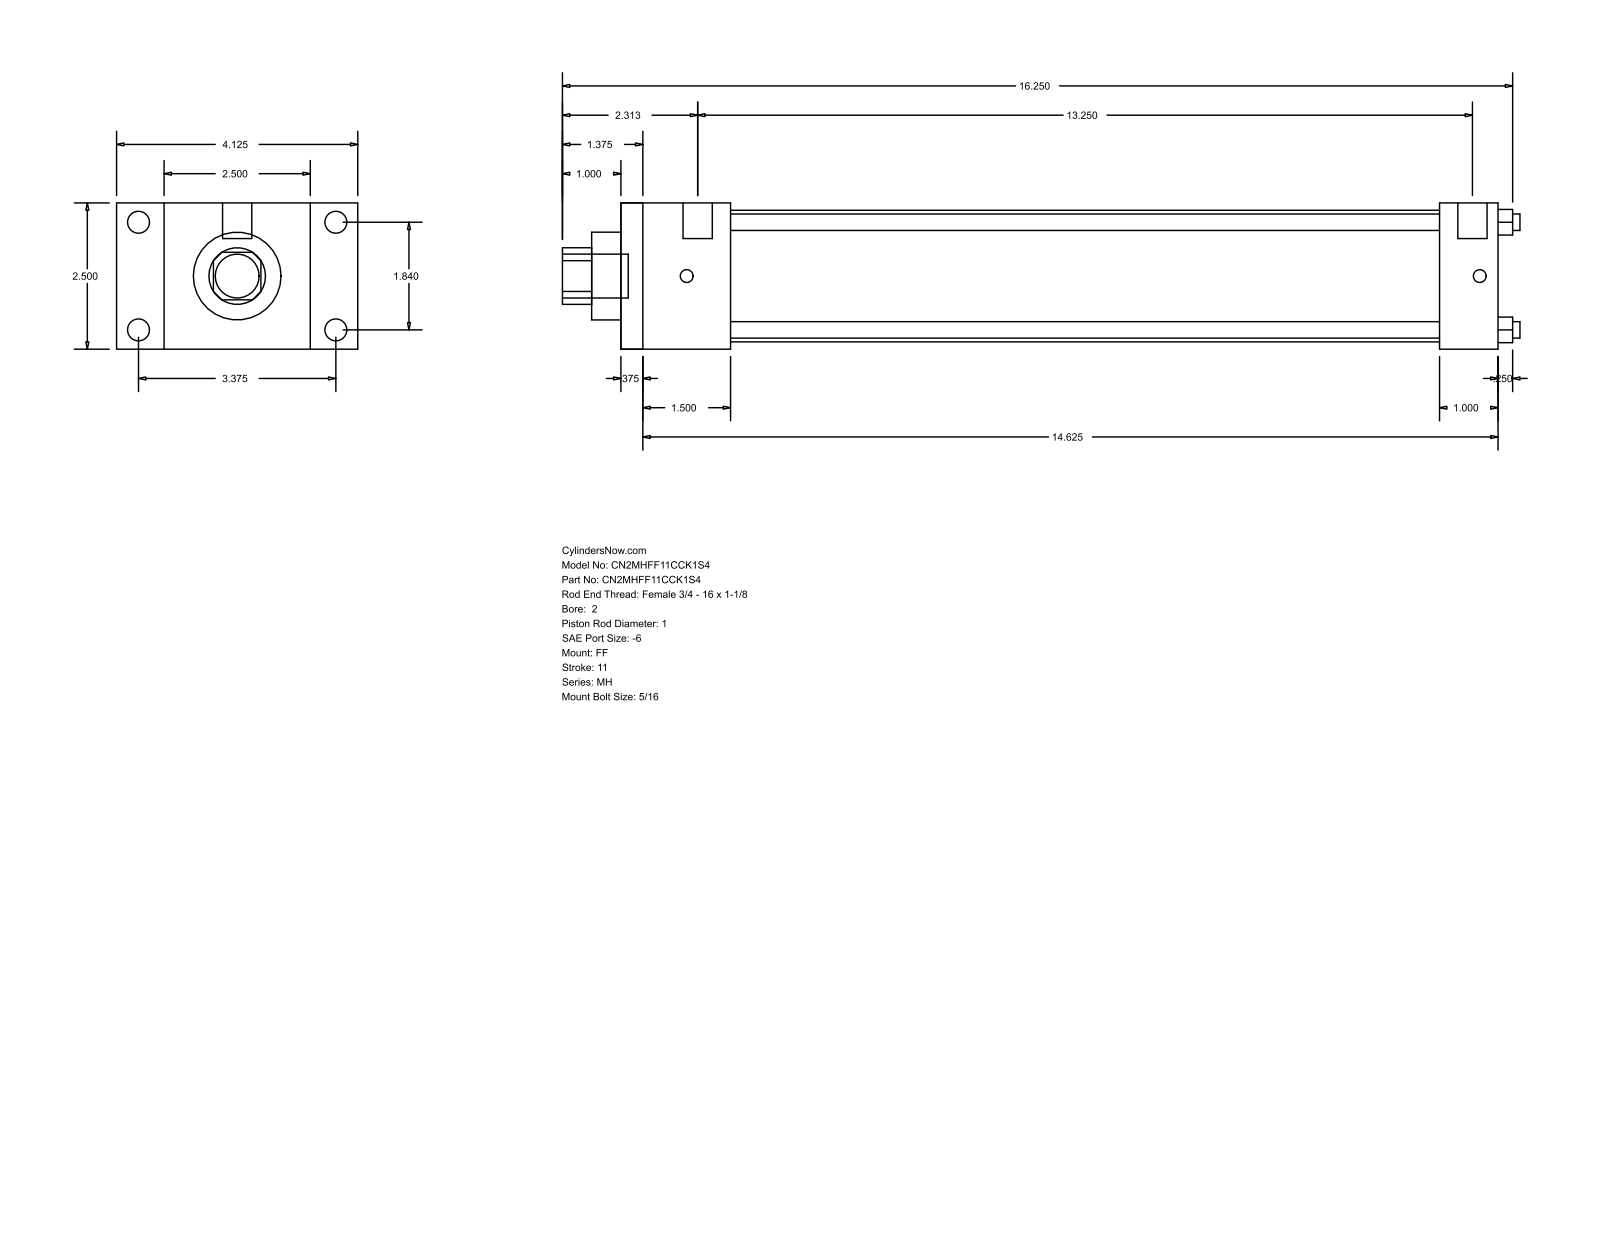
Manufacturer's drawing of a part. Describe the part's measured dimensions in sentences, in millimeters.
The part is named "MH_FF__0200_1". Its 3-D file was written by "GSSL Pune (CONFIG_CONTROL_DESIGN)". It is 0 solids with 92 faces: 64 planar, 28 cylindrical and 0 other. Overall it measures 415.93 by 104.78 by 63.5 millimeters. Round holes: 4 of diameter 7.14, 1 of diameter 25.4, 1 of diameter 38.1, 1 of diameter 57.15. Round bosses or shafts: 4 of diameter 9.53, 4 of diameter 5.56, 2 of diameter 12.7, 1 of diameter 19.05. Partial cylindrical surfaces (rounded edges, fillets, slot ends): 1 of radius 12.29. The main face-to-face distances are 63.5, 381, 9.52, 371.48, 20.64, 25.4, 47.63, 355.6, 38.11, 346.08. The hole center spacings are 33.05, 46.74, 66.1.
